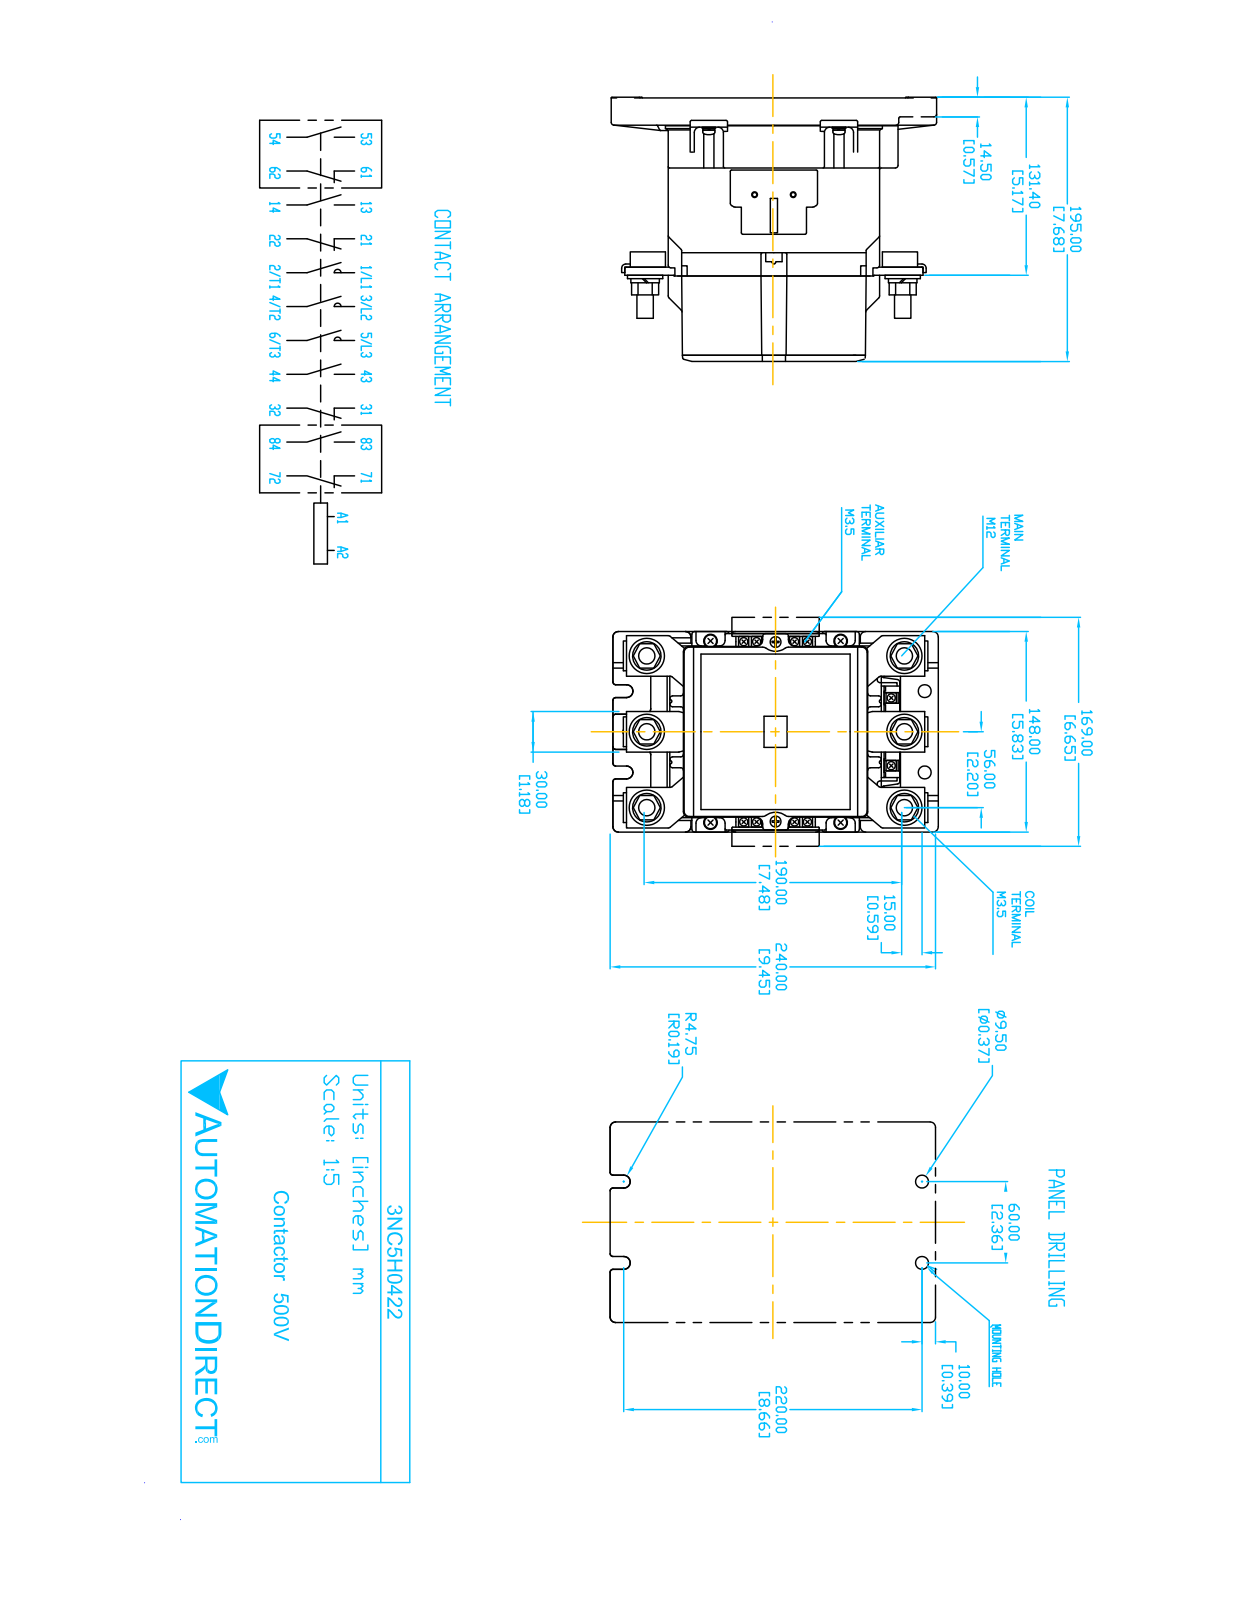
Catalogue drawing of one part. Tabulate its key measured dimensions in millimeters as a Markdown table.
| quantity | value |
| --- | --- |
| part name | 3NC5H0422 |
| STEP written by | SolidWorks 2018 (AUTOMOTIVE_DESIGN) |
| units | millimeters |
| bodies | 20 solids, 375 faces (261 planar, 114 cylindrical, 0 other) |
| overall size | 240 × 195 × 149 |
| volume | 4 197 000 mm³ |
| surface area | 278 100 mm² |
| round holes (diameter × count) | 12 × 6, 8 × 2, 10 × 2 |
| partial cylindrical surfaces (radius × count) | 2 × 26, 4 × 16, 1 × 12, 0.8 × 8, 5 × 6, 0.5 × 2 |
| main face-to-face distances | 115, 11, 126, 10, 146, 137, 80, 195, 21, 94 |
| hole center spacings | 57, 95.6, 116.8, 157, 198.4, 190, 30.8, 33.6 |
